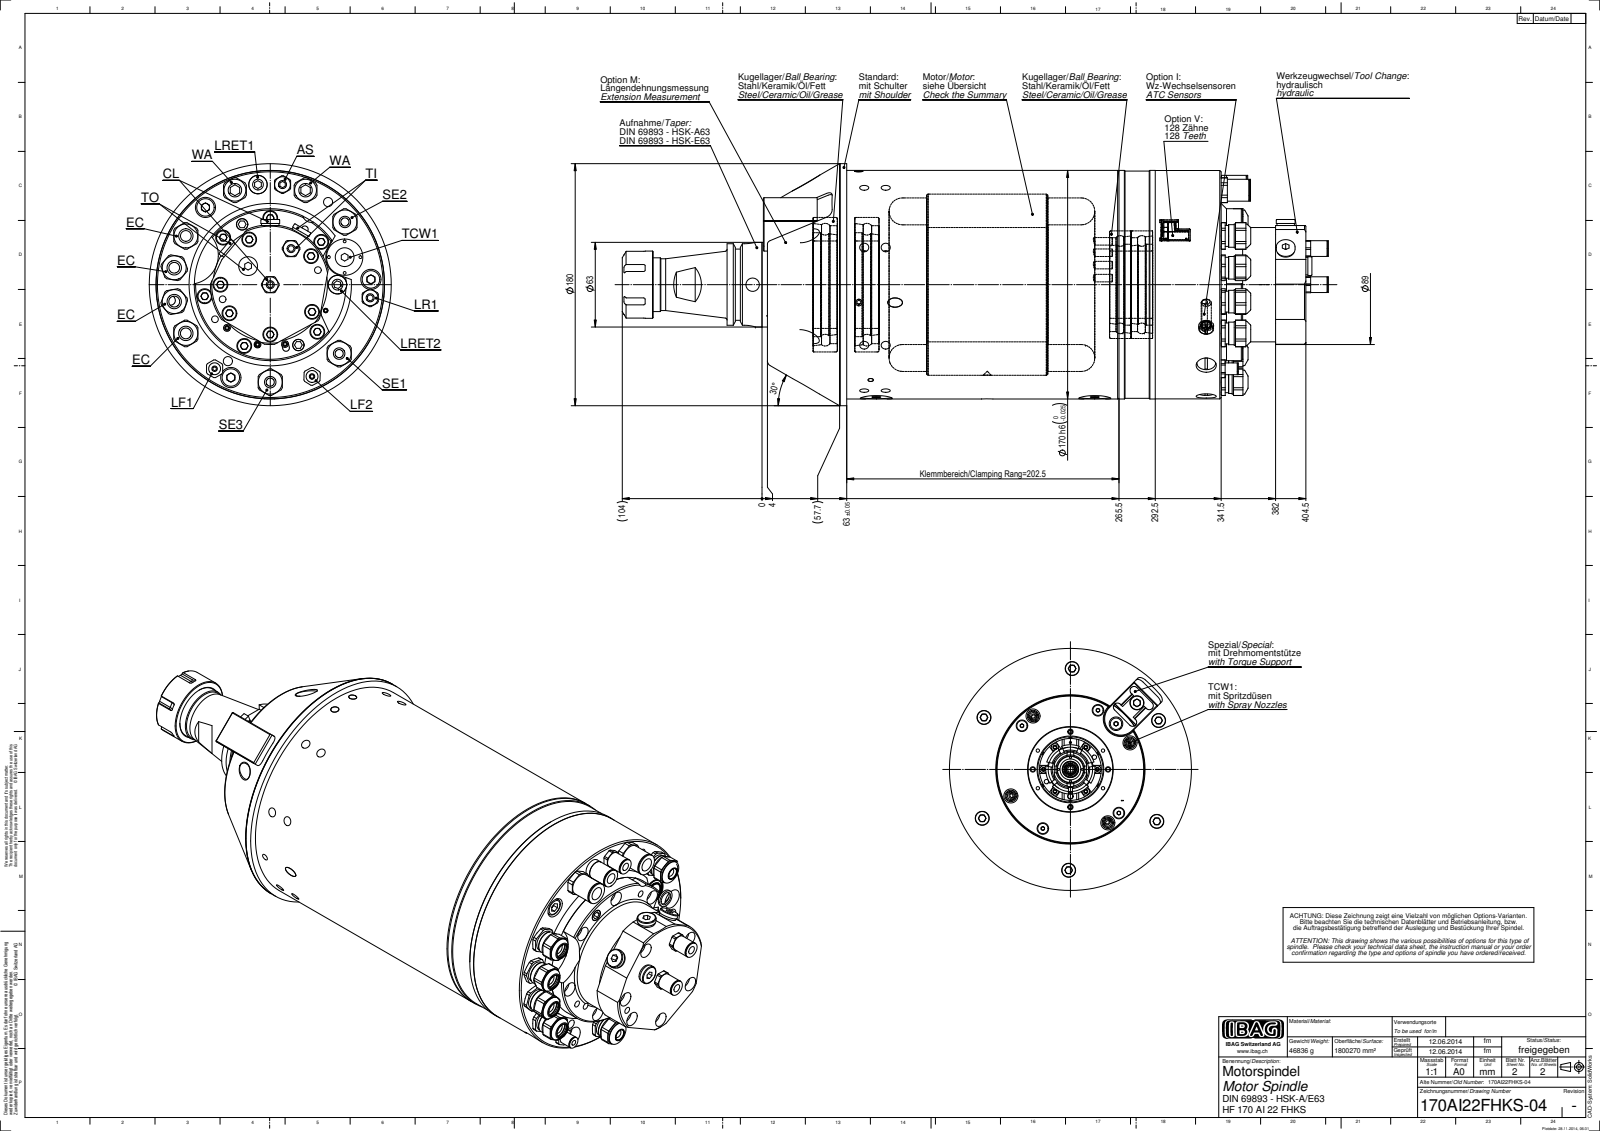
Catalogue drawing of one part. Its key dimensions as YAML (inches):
part_name: "170AI22FHKS-04"
step_written_by: "SolidWorks 2014 (CONFIG_CONTROL_DESIGN)"
units: inches
bodies: {solids: 0, faces: 1513, planar: 621, cylindrical: 586, other: 306}
overall_size: [20.694, 7.087, 7.087]
round_holes:
  - {diameter: 0.268, count: 20}
  - {diameter: 0.433, count: 12}
  - {diameter: 0.335, count: 8}
  - {diameter: 0.197, count: 7}
  - {diameter: 0.236, count: 7}
  - {diameter: 0.409, count: 7}
  - {diameter: 0.591, count: 7}
  - {diameter: 0.315, count: 6}
  - {diameter: 0.083, count: 4}
  - {diameter: 0.177, count: 4}
  - {diameter: 0.394, count: 4}
  - {diameter: 0.421, count: 4}
round_bosses_or_shafts:
  - {diameter: 0.701, count: 7}
  - {diameter: 0.661, count: 7}
  - {diameter: 0.614, count: 7}
  - {diameter: 0.512, count: 7}
  - {diameter: 0.551, count: 5}
  - {diameter: 0.461, count: 4}
  - {diameter: 0.394, count: 4}
  - {diameter: 0.301, count: 4}
partial_cylinders:
  - {radius: 0.039, count: 12}
  - {radius: 0.39, count: 7}
  - {radius: 0.26, count: 6}
  - {radius: 0.118, count: 4}
  - {radius: 0.315, count: 4}
  - {radius: 0.098, count: 2}
  - {radius: 0.197, count: 2}
  - {radius: 0.276, count: 2}
face_to_face_distances: [9.232, 11.161, 1.929, 2.323, 13.445, 13.287, 2.126, 11.358, 15.768, 13.642]
hole_center_spacings: [2.953, 0.63, 5.115, 5.008, 0.694, 1.102, 1.404, 1.429]
